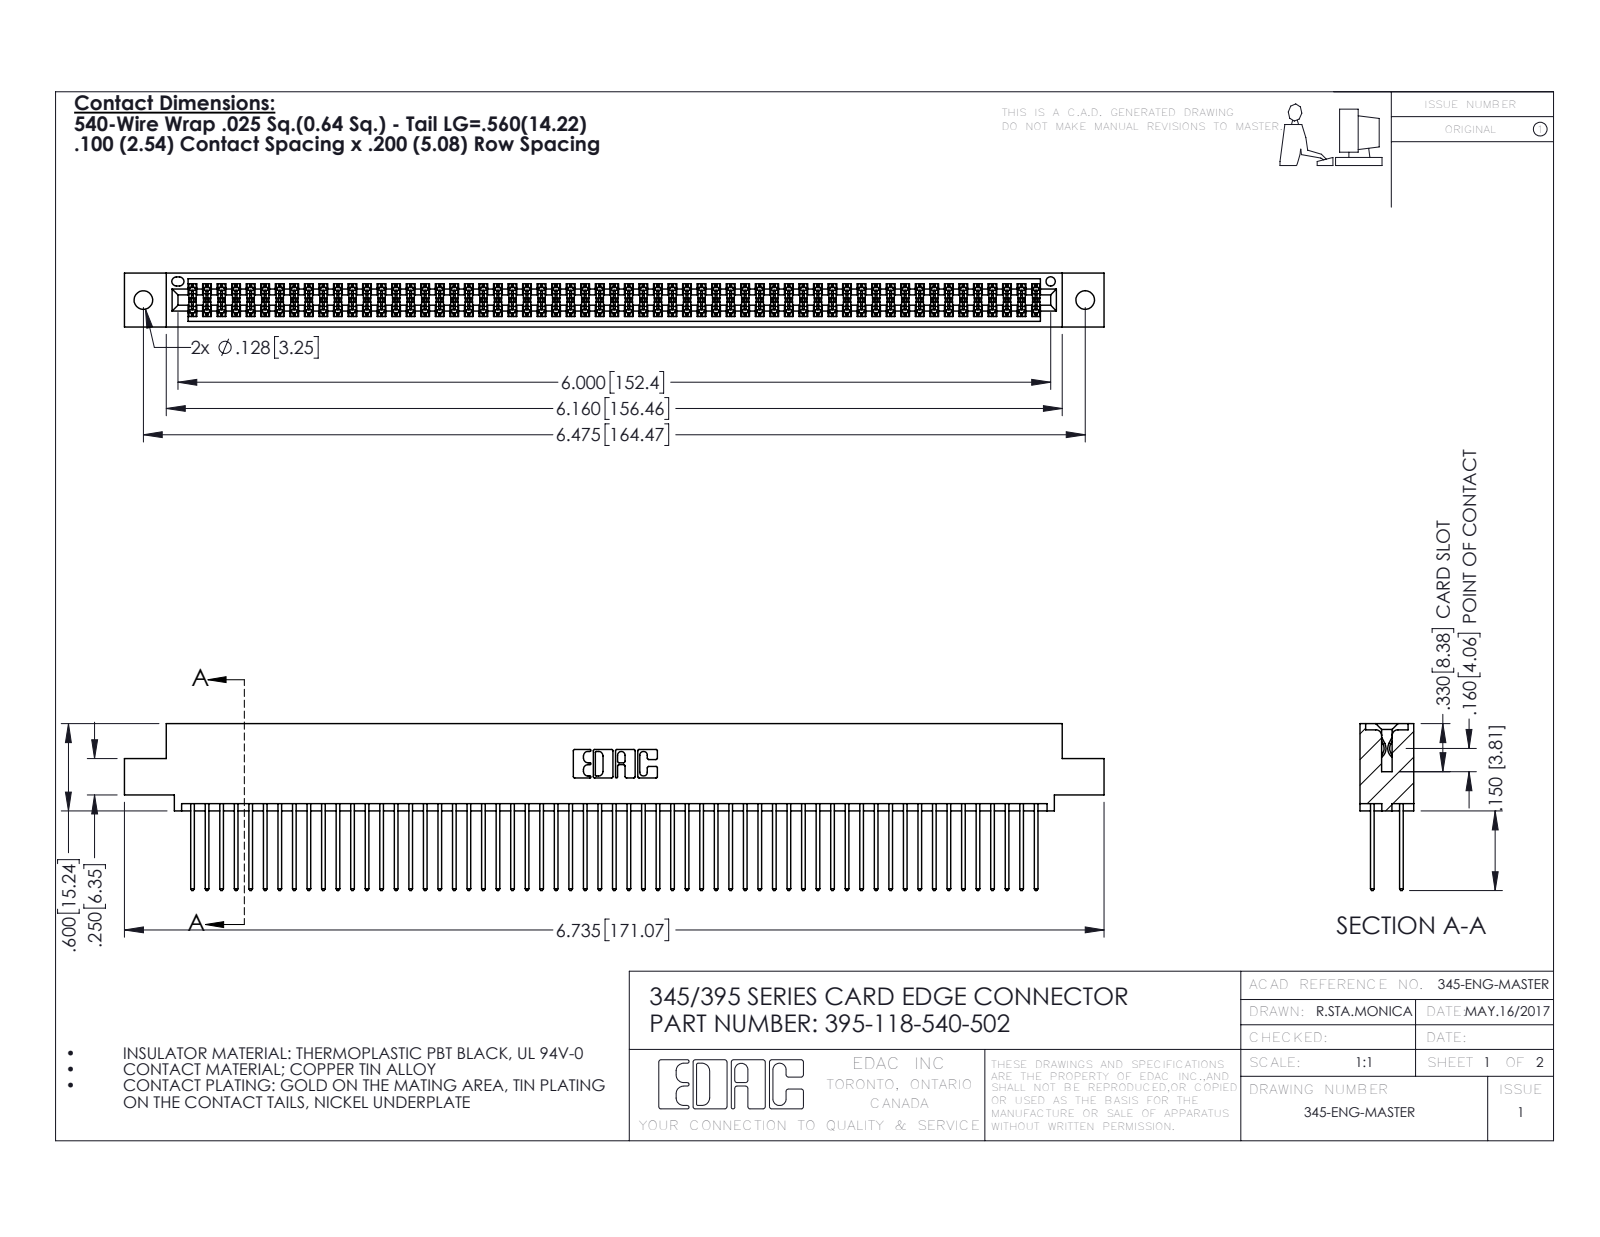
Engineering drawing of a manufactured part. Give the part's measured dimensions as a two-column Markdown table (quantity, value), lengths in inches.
| quantity | value |
| --- | --- |
| part name | 345-292-001_345-293-140; 395-118-540-502; 345 Part_0.110 Offset - 0.128 Dia |
| STEP written by | SolidWorks 2016 (CONFIG_CONTROL_DESIGN) |
| units | inches |
| bodies | 119 solids, 6030 faces (3978 planar, 2052 cylindrical, 0 other) |
| overall size | 6.735 × 1.147 × 0.37 |
| volume | 1.044 in³ |
| surface area | 42.66 in² |
| round holes (diameter × count) | 0.128 × 2, 0.064 × 1 |
| partial cylindrical surfaces (radius × count) | 0.006 × 177, 0.01 × 118, 0.01 × 22, 0.007 × 6, 0.031 × 6, 0.026 × 3, 0.014 × 2, 0.019 × 2 |
| main face-to-face distances | 0.298, 0.072, 0.2, 0.098, 0.272, 0.025, 0.37, 0.225, 0.175, 0.149 |
| hole center spacings | 0.27, 6.239, 6.475 |
